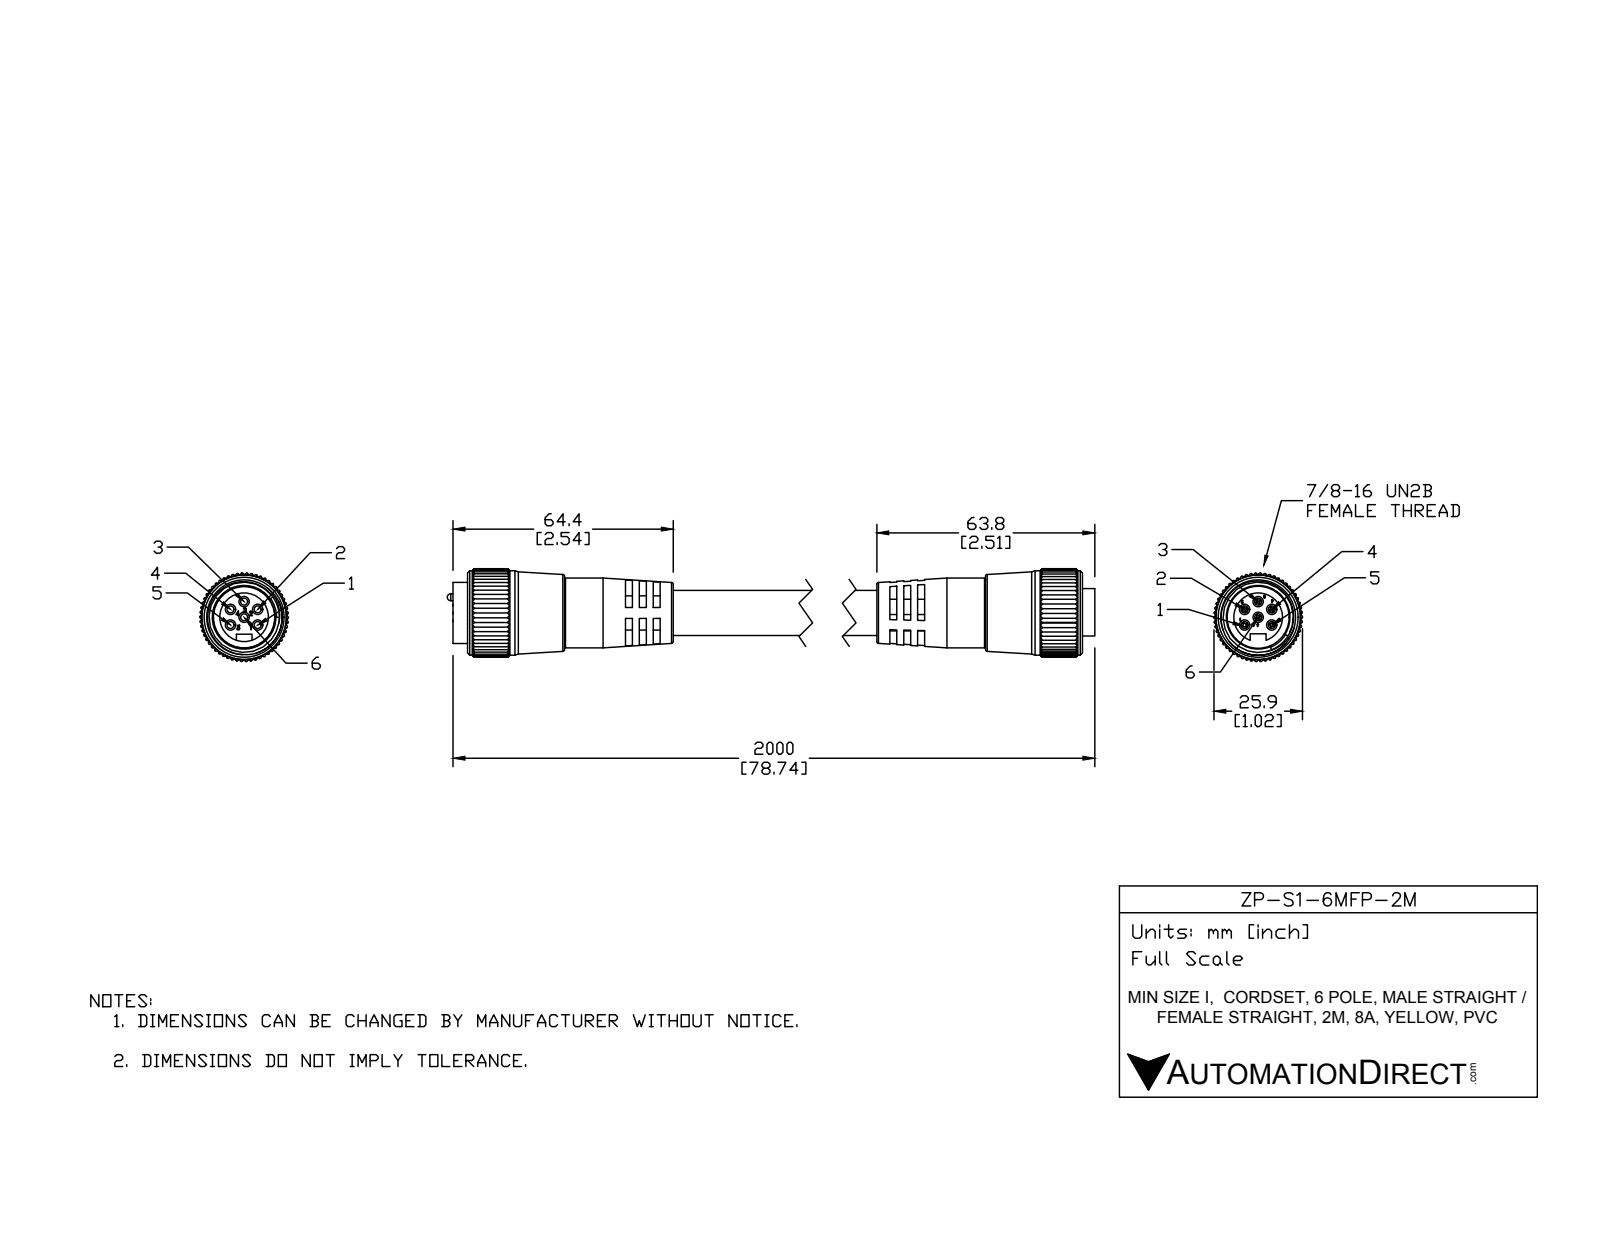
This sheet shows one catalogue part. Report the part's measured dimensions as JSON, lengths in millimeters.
{"part_name": "ZP-S1-6MFP-2M", "step_written_by": "SolidWorks 2015 (AUTOMOTIVE_DESIGN)", "units": "millimeters", "bodies": {"solids": 10, "faces": 1226, "planar": 452, "cylindrical": 636, "other": 138}, "overall_size": [229.66, 25.84, 25.83], "volume_mm3": 50878, "surface_area_mm2": 23497, "round_holes": [[3.05, 6], [19.96, 1], [20.45, 1], [21, 1]], "round_bosses_or_shafts": [[2, 6], [24.68, 1], [20.4, 1], [19.5, 1], [17.88, 1], [14.22, 1], [9.91, 1], [3.05, 1]], "partial_cylinders_radius": [[0.25, 165], [2.29, 1], [5.25, 1], [12.93, 1]], "face_to_face_distances": [2, 4.02, 117.68, 113.65, 4.03, 125.74, 59.84, 4.04, 121.7, 121.72], "hole_center_spacings": [4.57, 4.56, 7.91, 7.92, 9.14]}
